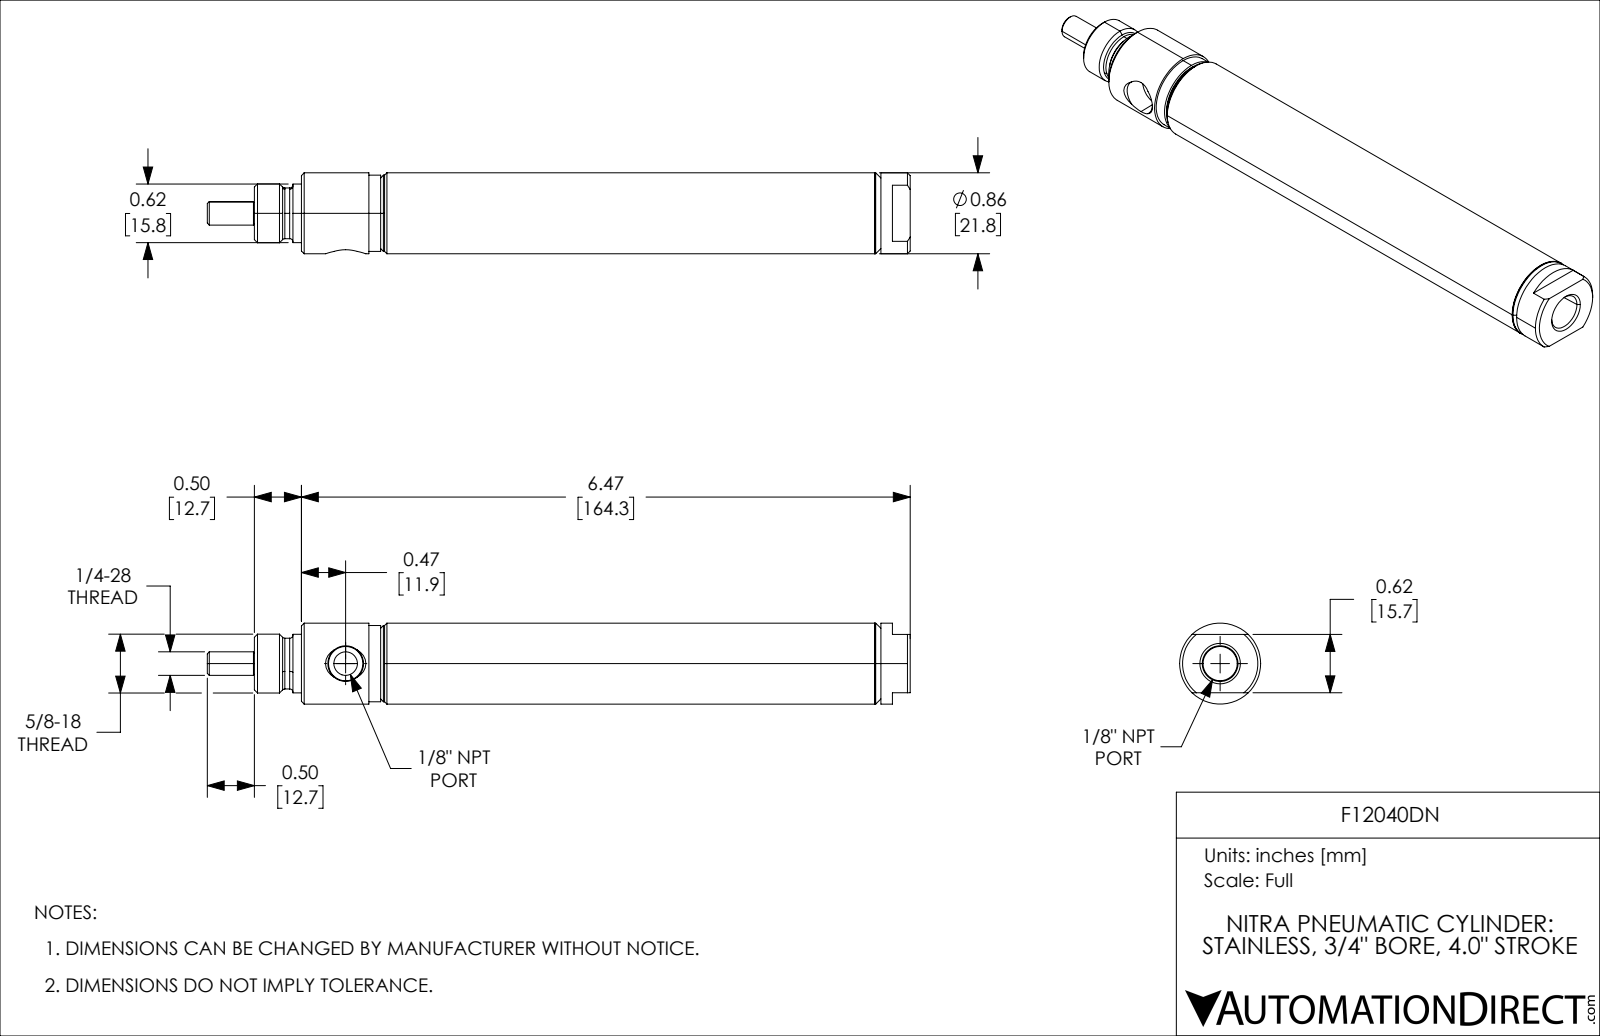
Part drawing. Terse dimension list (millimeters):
name: F12040DN_9; F12040DN; F12040DN_5; F12040DN_7 (+1 more)
written by: SolidWorks 2021 (CONFIG_CONTROL_DESIGN)
unit: mm
bodies: 4 solids, 124 faces (22 planar, 46 cylindrical, 56 other)
size: 189.71 × 21.84 × 21.84
volume: 34 934 mm³; area: 29 100 mm²
holes: 1× ⌀6.35, 1× ⌀6.95, 1× ⌀12.7, 1× ⌀17.83
bosses: 1× ⌀21.84, 1× ⌀20.57, 1× ⌀19.35, 1× ⌀15.88, 1× ⌀15.81, 1× ⌀13.68, 1× ⌀6.35, 1× ⌀5.84
face distances: 21.43, 101.6, 123.03, 136.52, 34.92, 13.49, 12.7, 27.79, 129.39, 150.82
